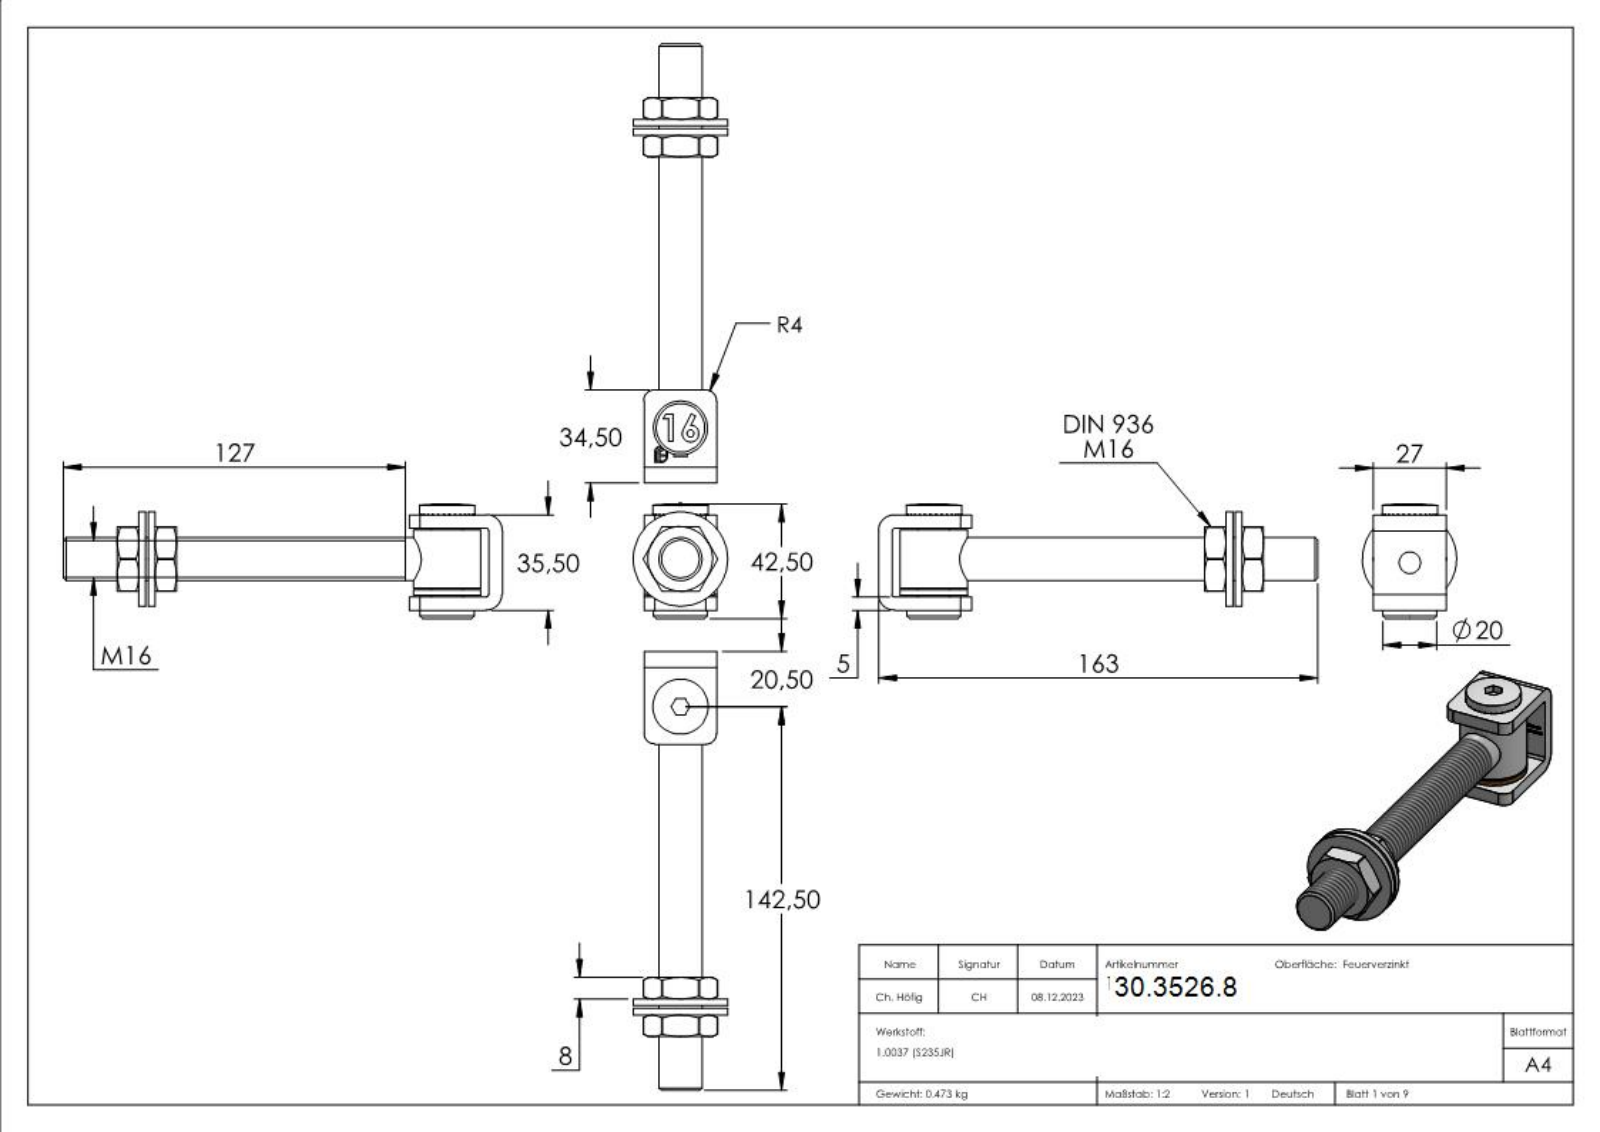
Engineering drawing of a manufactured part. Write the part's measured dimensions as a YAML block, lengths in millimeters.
part_name: "130-M16; 130-Mxx Teil6; Torband Teil3_130-M16 Teil3; 130-Mxx Teil6_130-M16 Teil6 (+8 more)"
step_written_by: "SolidWorks 2018 (CONFIG_CONTROL_DESIGN)"
units: millimeters
bodies: {solids: 9, faces: 389, planar: 187, cylindrical: 56, other: 146}
overall_size: [22000, 21000, 21000]
volume: 61764
surface_area: 27397
round_holes:
  - {diameter: 5, count: 1}
  - {diameter: 12.5, count: 1}
  - {diameter: 14, count: 1}
  - {diameter: 17, count: 1}
round_bosses_or_shafts:
  - {diameter: 16, count: 2}
  - {diameter: 35, count: 1}
  - {diameter: 25, count: 1}
  - {diameter: 20, count: 1}
  - {diameter: 11.8, count: 1}
  - {diameter: 6, count: 1}
partial_cylinders:
  - {radius: 0.5, count: 6}
  - {radius: 1, count: 2}
  - {radius: 4, count: 2}
  - {radius: 6, count: 2}
face_to_face_distances: [5, 4, 3, 7, 30.5, 0.5, 35.5, 23, 12, 30]
